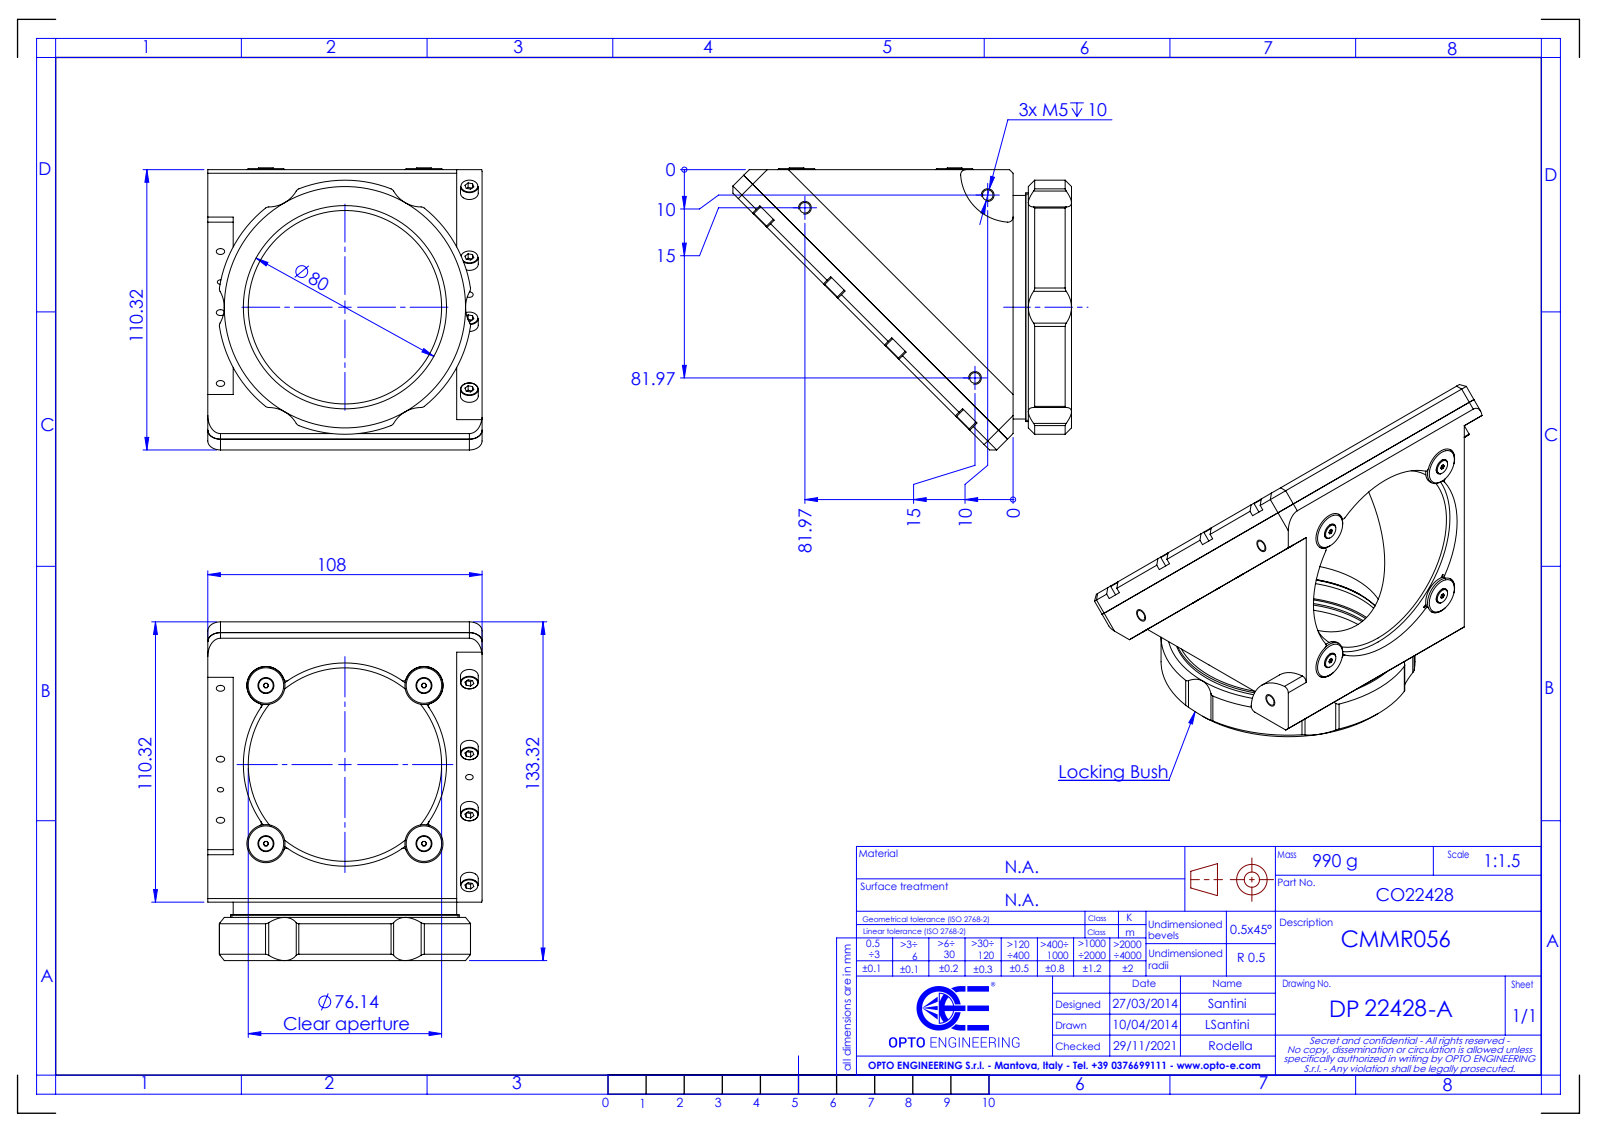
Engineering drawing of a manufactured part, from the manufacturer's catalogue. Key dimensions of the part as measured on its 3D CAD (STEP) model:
Part name (STEP PRODUCT): DP22428-A_CMMR056
STEP written by: SolidWorks 2021 (CONFIG_CONTROL_DESIGN)
Units: millimetres
Bodies: 0 solids, 369 faces (146 planar, 145 cylindrical, 78 other)
Overall size (bounding box): 133.32 × 111.04 × 108
Round holes (diameter × count): ⌀3.3 ×8, ⌀4.2 ×3, ⌀3 ×2, ⌀76.14 ×2, ⌀80 ×2, ⌀2.5 ×1, ⌀80.6 ×1, ⌀82.2 ×1, ⌀84 ×1, ⌀88 ×1
Round bosses / shafts (diameter × count): ⌀7 ×8, ⌀15 ×4, ⌀5.75 ×4, ⌀90 ×1
Partial cylindrical surfaces — rounded edges, fillets, slot ends (radius × count): R2 ×14, R1 ×8, R12.5 ×6, R4 ×4, R5 ×4, R20 ×1, R50 ×1
Main face-to-face distances: 8, 10, 98, 88, 7, 15, 23, 108, 14, 22
Hole centre spacings: 98, 17, 39.44, 56.44, 73.44, 99.46, 105.64, 113.09
